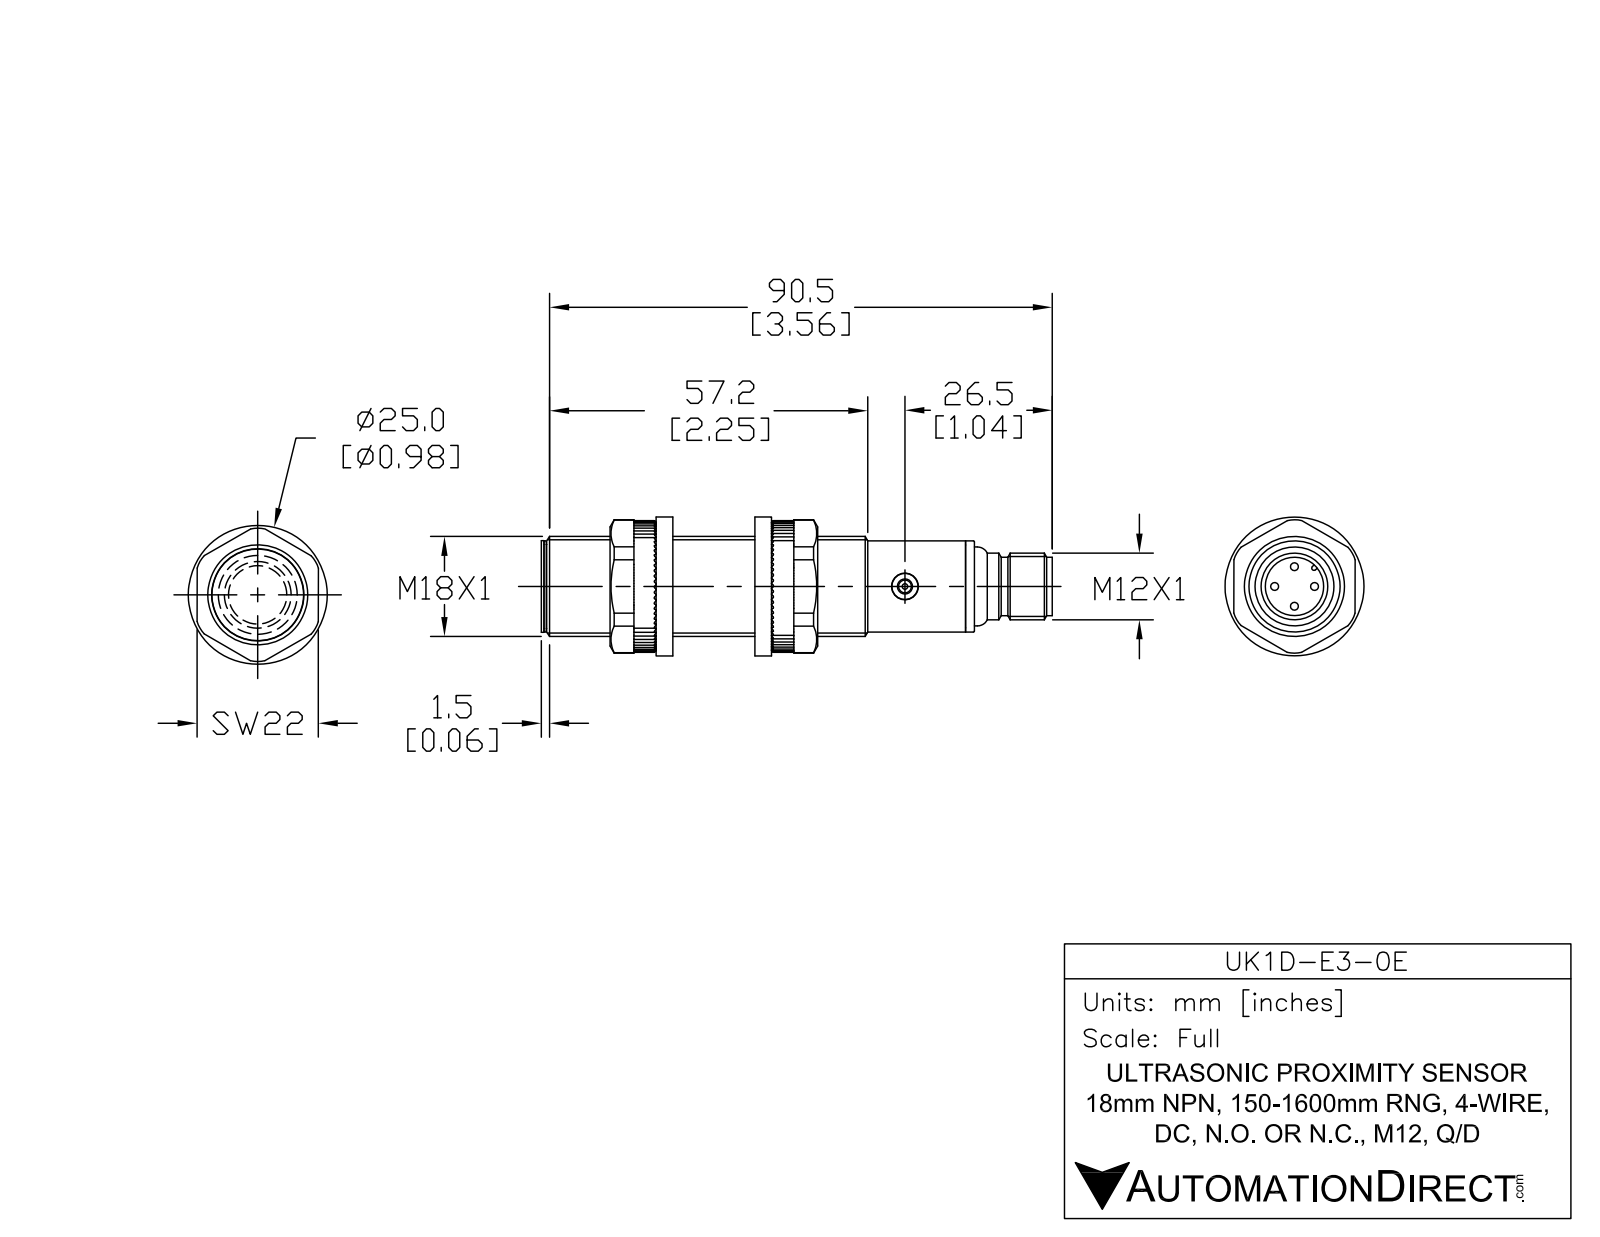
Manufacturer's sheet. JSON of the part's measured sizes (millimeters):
{"part_name": "UK1D-E3-0E", "step_written_by": "SolidWorks 2017 (AUTOMOTIVE_DESIGN)", "units": "millimeters", "bodies": {"solids": 6, "faces": 106, "planar": 21, "cylindrical": 48, "other": 37}, "overall_size": [91.6, 18, 18], "volume_mm3": 19700, "surface_area_mm2": 6890, "round_holes": [[2.7, 1], [4.7, 1], [7, 1], [8.3, 1], [9.5, 1]], "round_bosses_or_shafts": [[1, 4], [18, 1], [16.6, 1], [16.4, 1], [15.8, 1], [14.2, 1], [12, 1], [10.5, 1]], "partial_cylinders_radius": [[0.6, 1]], "face_to_face_distances": [75.1, 1, 76.1, 0.9, 76, 1.1, 4, 77.6, 77.5, 76.6]}
